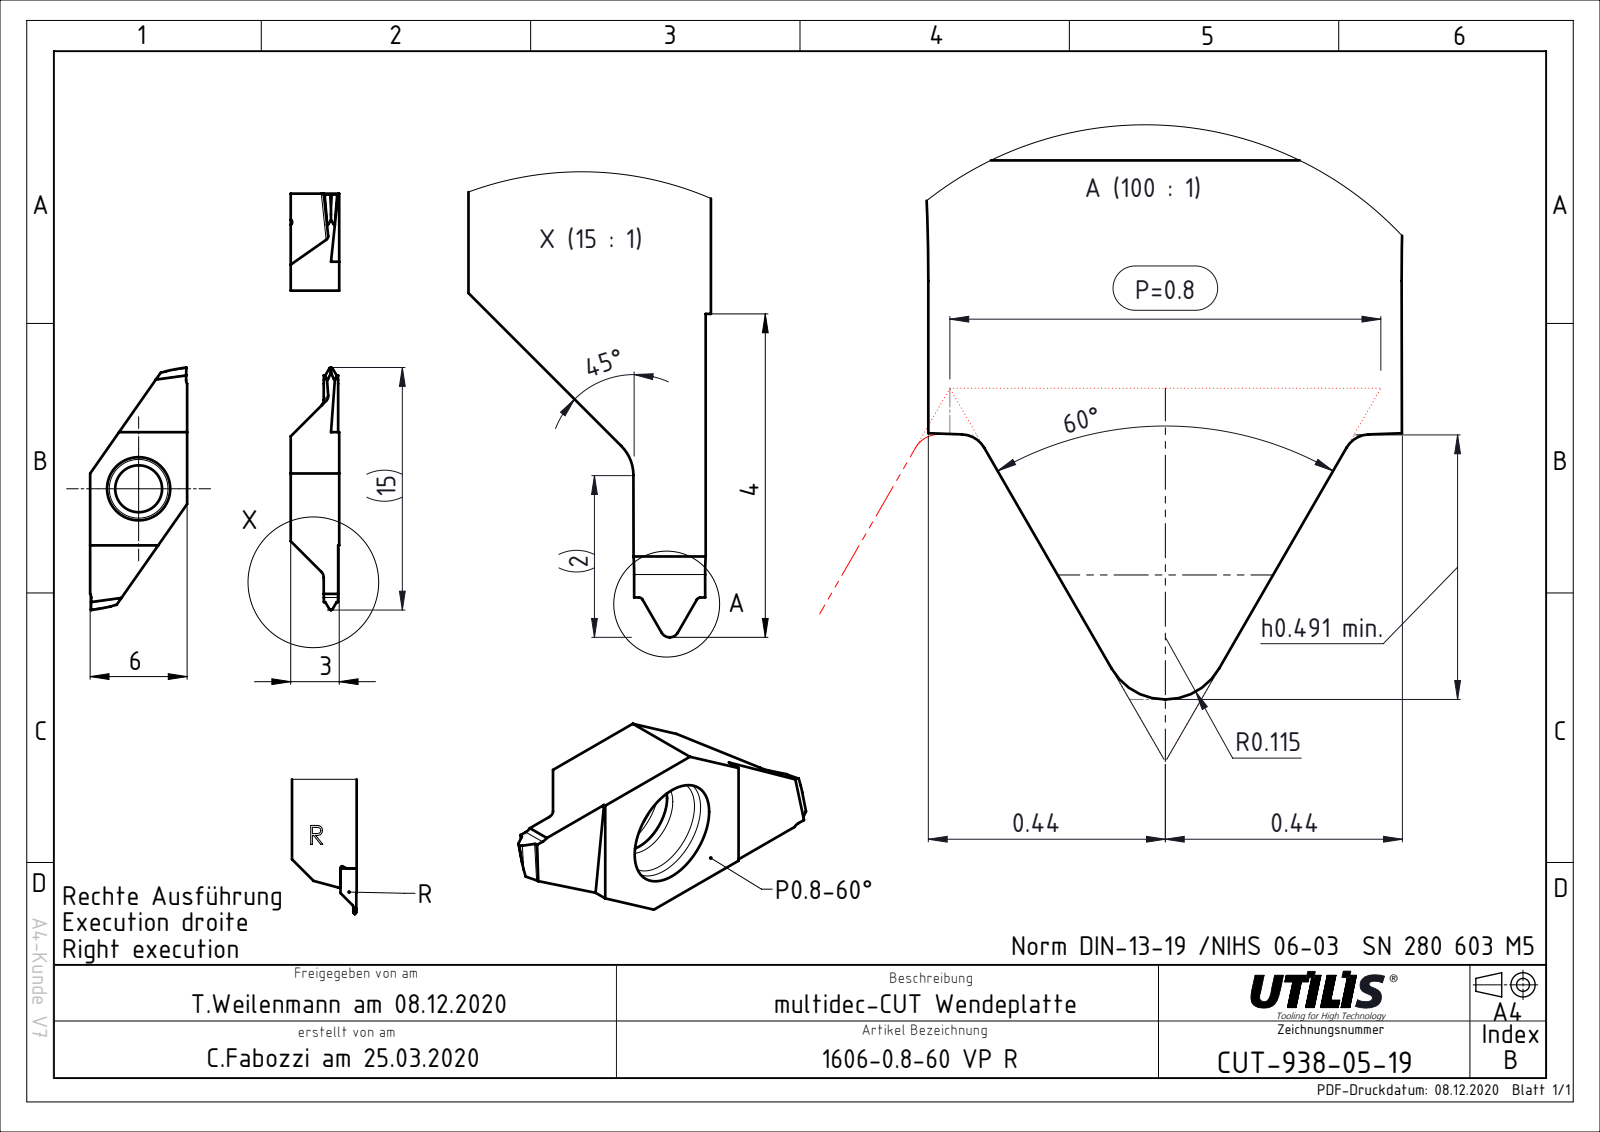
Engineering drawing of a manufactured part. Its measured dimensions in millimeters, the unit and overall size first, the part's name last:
Units: millimetres
Overall size (bounding box): 15 × 6 × 3
Round holes (diameter × count): ⌀2.9 ×1
Partial cylindrical surfaces — rounded edges, fillets, slot ends (radius × count): R0.12 ×4, R0.5 ×2
Main face-to-face distances: 6, 3, 0.73, 9, 11.22, 11.23, 12, 7, 12.55, 12.56
Volume: 123 mm³ · Surface area: 209 mm²
Bodies: 1 solid, 43 faces (24 planar, 14 cylindrical, 5 other)
Part name (STEP PRODUCT): CUT-938-05; ASME Y14.5
STEP written by: FormatWorks Professional (AP242_MANAGED_MODEL_BASED_3D_ENGINEERING_MIM_LF)
